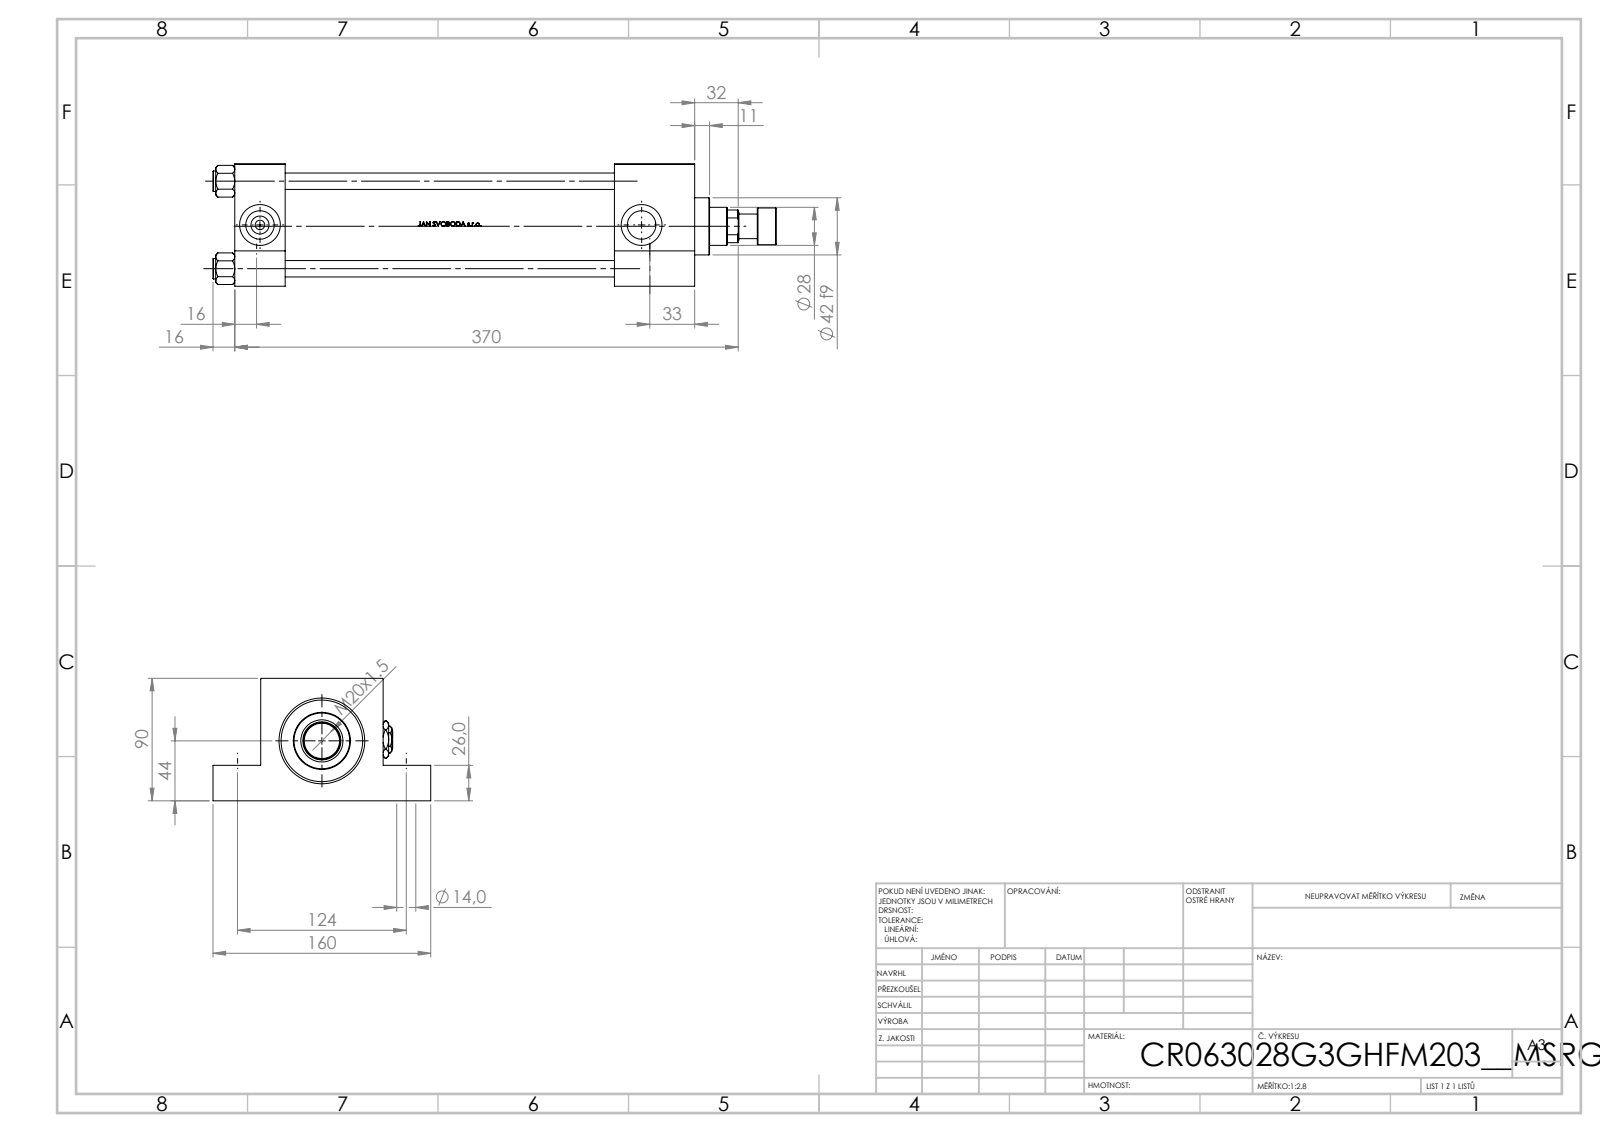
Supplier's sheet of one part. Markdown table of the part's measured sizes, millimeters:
| quantity | value |
| --- | --- |
| part name | V215CR_ROD_END_F; V215_VC_A; Zatka_pro_OIL_PORT; V215CR_G_Body (+3 more) |
| STEP written by | SolidWorks 2019 (CONFIG_CONTROL_DESIGN) |
| units | millimeters |
| bodies | 14 solids, 1198 faces (482 planar, 136 cylindrical, 580 other) |
| overall size | 414 × 160 × 90 |
| volume | 1 431 000 mm³ |
| surface area | 327 164 mm² |
| round holes (diameter × count) | 12 × 4, 14 × 4, 7 × 2, 20.96 × 2, 30 × 2, 18.5 × 1, 28 × 1, 31 × 1, 50 × 1, 60 × 1, 63 × 1 |
| round bosses / shafts (diameter × count) | 15 × 4, 69 × 1, 42 × 1, 27 × 1, 18 × 1 |
| main face-to-face distances | 90, 37, 301, 338, 59, 279, 242, 64, 26, 35 |
| hole center spacings | 64.3, 44.77, 46.18, 90.93, 124, 289, 314.48, 280.5 |
